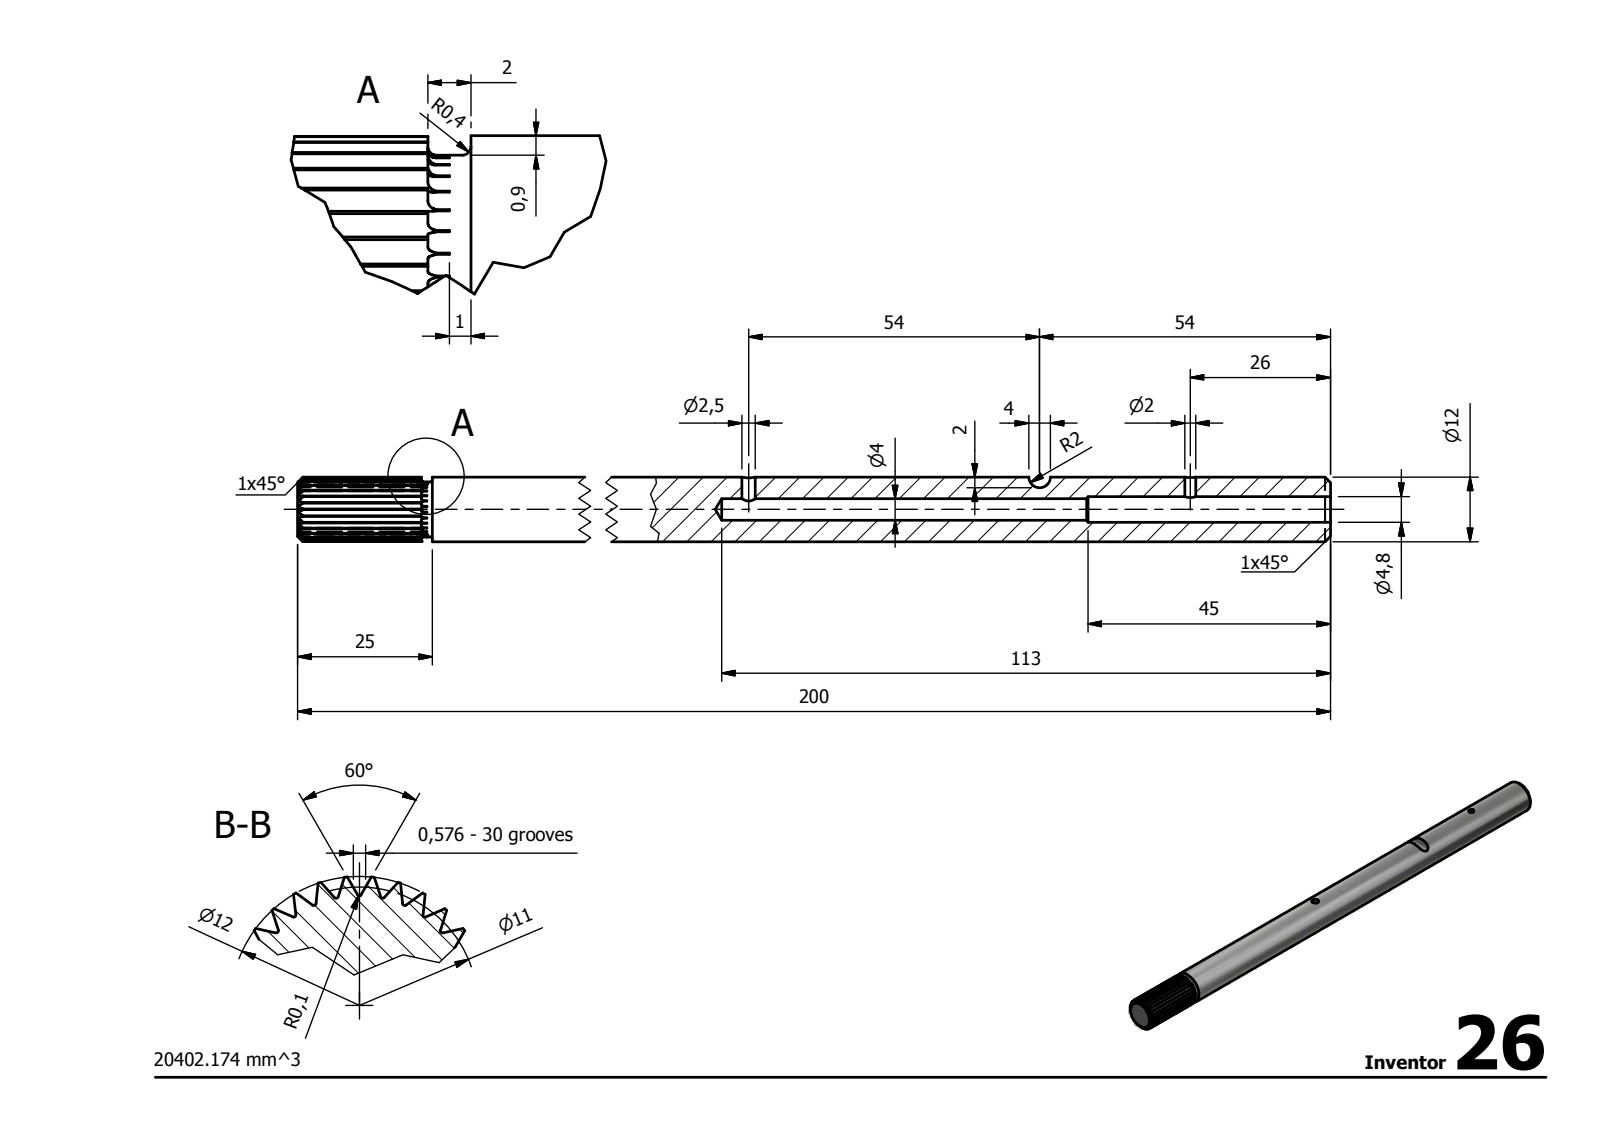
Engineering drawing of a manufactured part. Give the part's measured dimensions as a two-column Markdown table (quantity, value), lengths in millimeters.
| quantity | value |
| --- | --- |
| STEP written by | Autodesk Inventor 2014 (AUTOMOTIVE_DESIGN) |
| units | millimeters |
| bodies | 1 solid, 225 faces (123 planar, 67 cylindrical, 35 other) |
| overall size | 200 × 12 × 12 |
| volume | 20 401 mm³ |
| surface area | 9 988 mm² |
| round holes (diameter × count) | 2 × 1, 2.5 × 1, 4 × 1, 4.8 × 1 |
| round bosses / shafts (diameter × count) | 12 × 1, 10.2 × 1 |
| partial cylindrical surfaces (radius × count) | 0.1 × 30, 2 × 1 |
| main face-to-face distances | 5, 200, 25, 175, 23, 2, 177, 1, 24, 176 |
| hole center spacings | 82 |
